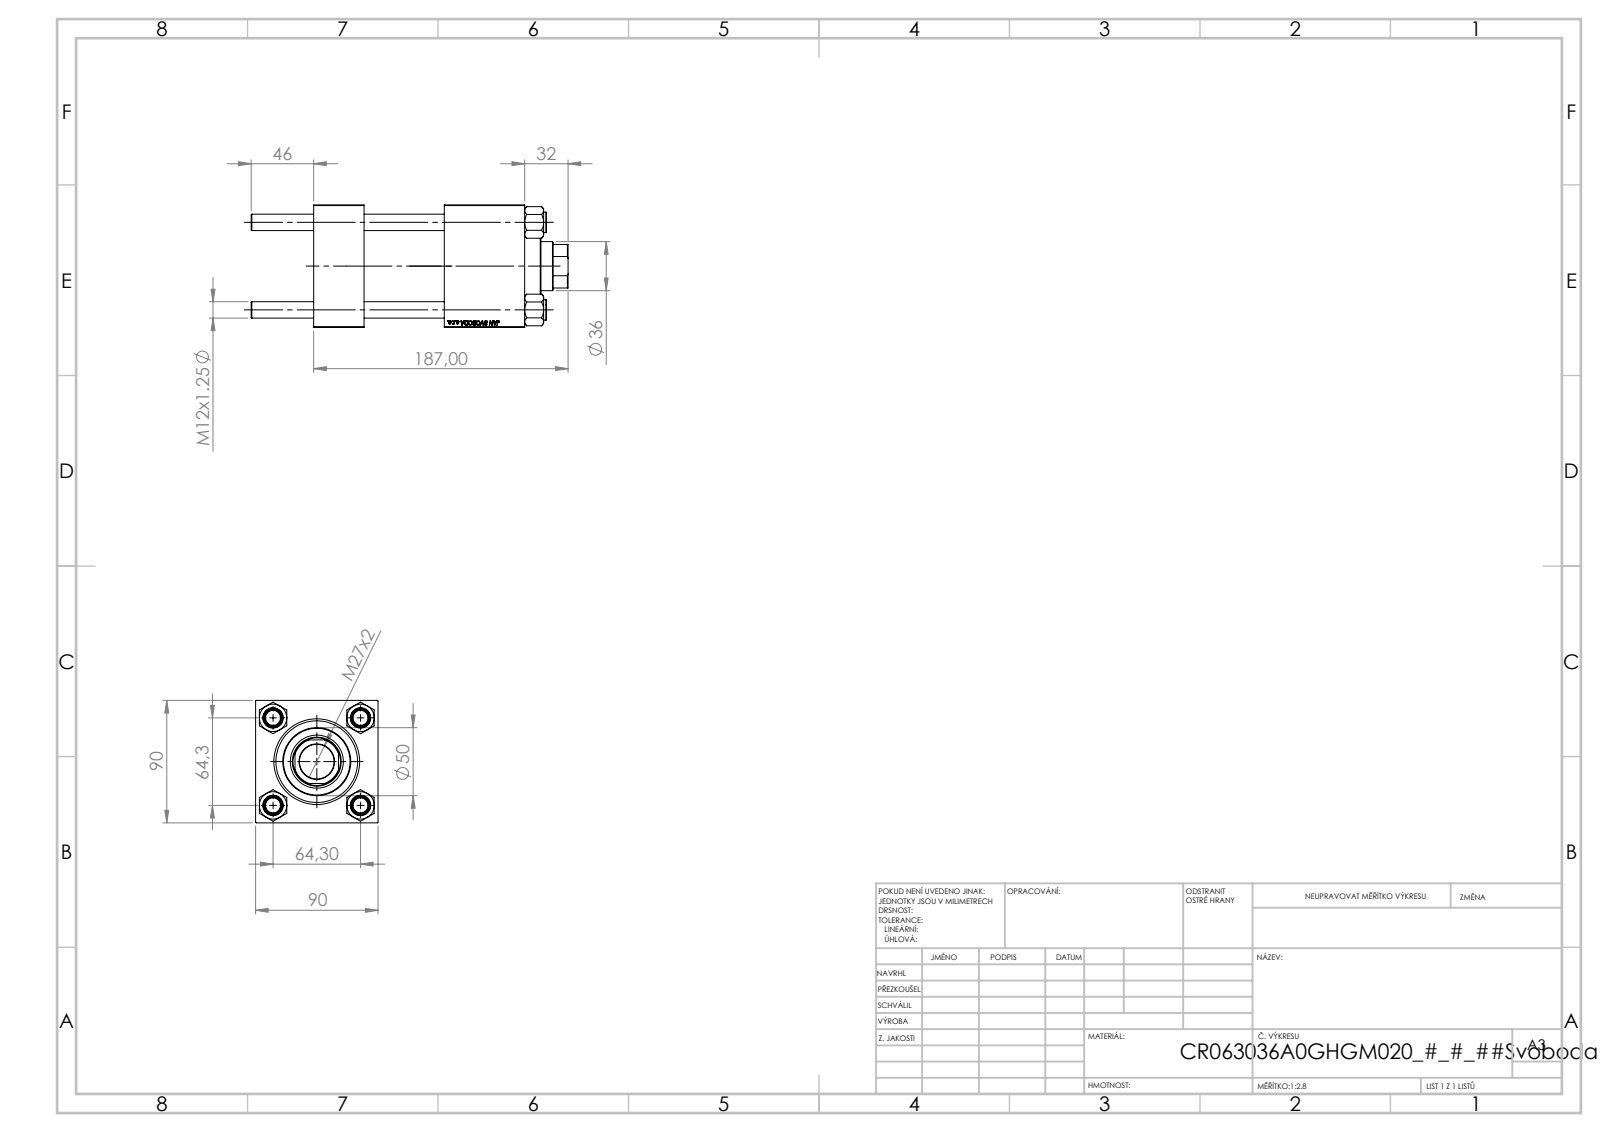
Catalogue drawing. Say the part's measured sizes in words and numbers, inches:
The part is named "V215CR_VCP; CR025_012_A_0_G_A_G_M_020_+#_##_TYCINKA; V215_VC_A; V215CR_BODY_A (+1 more)". Its 3-D file was written by "SolidWorks 2019 (CONFIG_CONTROL_DESIGN)". It is 11 solids with 1134 faces: 520 planar, 78 cylindrical and 536 other. Overall it measures 9.173 by 3.543 by 3.543 inches. Its volume is 61.15 cubic inches and its surface area 310.6 square inches. Round holes: 4 of diameter 0.472, 2 of diameter 0.276, 2 of diameter 0.825, 2 of diameter 1.181, 1 of diameter 1.004, 1 of diameter 1.417, 1 of diameter 1.535, 1 of diameter 1.969, 1 of diameter 2.362, 1 of diameter 2.48. Round bosses or shafts: 4 of diameter 0.591, 1 of diameter 2.717. Partial cylindrical surfaces (rounded edges, fillets, slot ends): 1 of radius 0.689. The main face-to-face distances are 3.543, 2.323, 1.457, 6.102, 4.646, 3.78, 4.972, 3.516, 1.193, 1.13. The hole center spacings are 1.79, 2.531, 3.58, 3.839.
